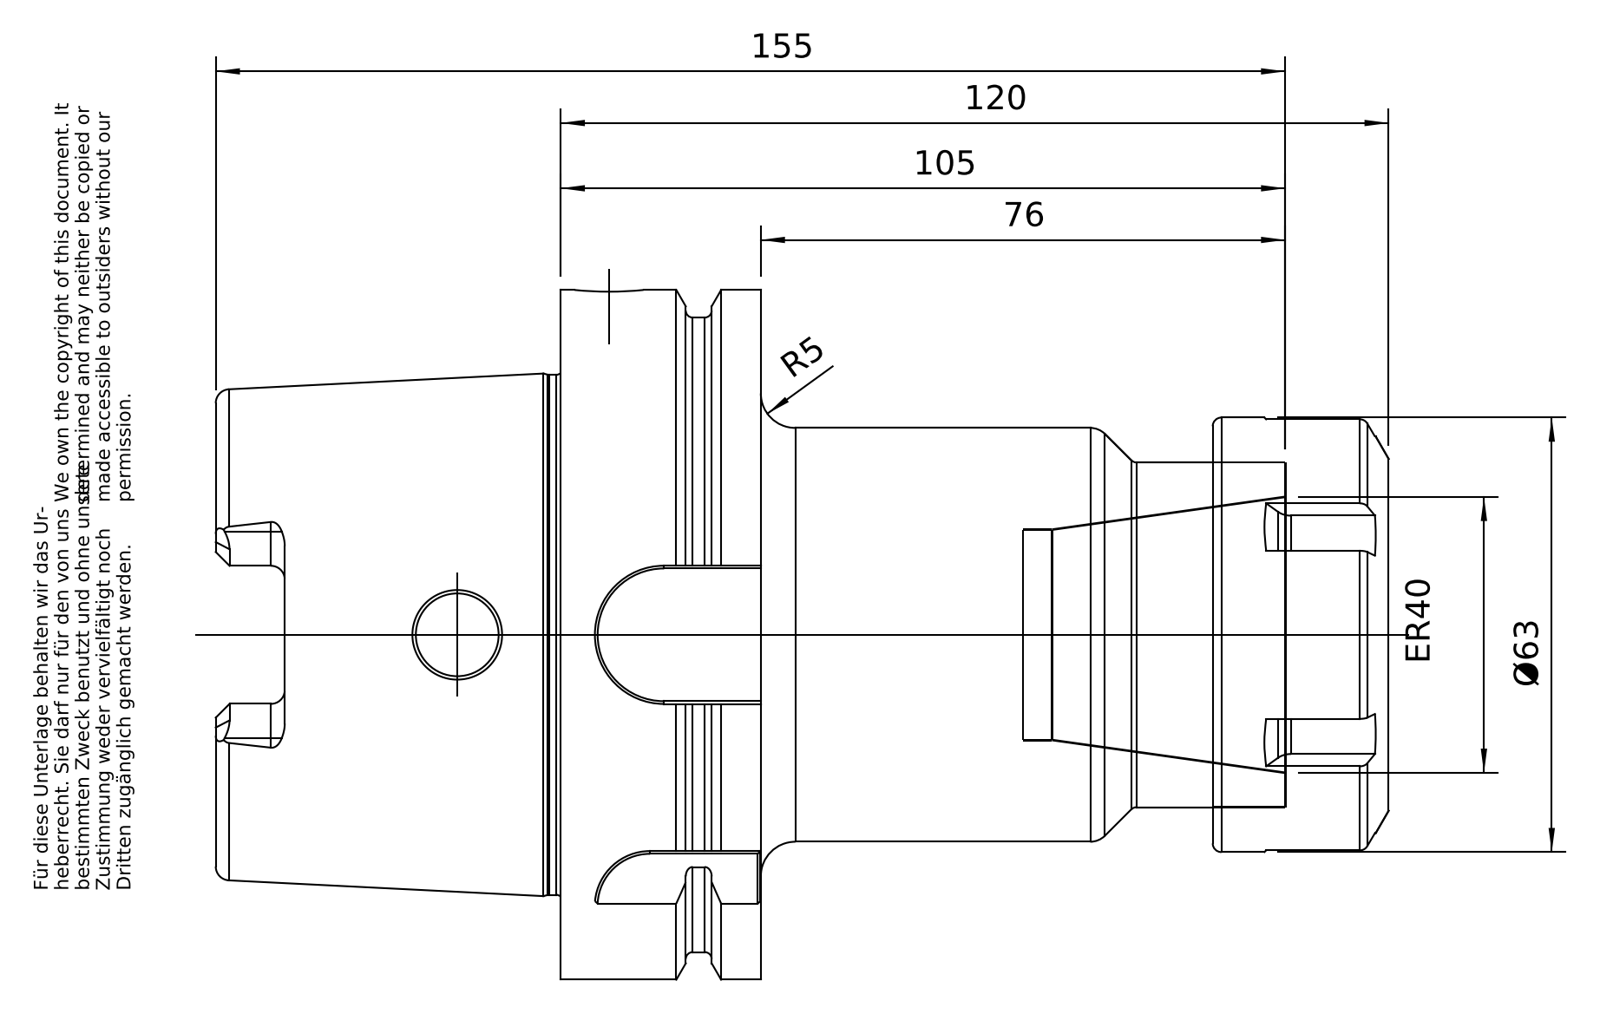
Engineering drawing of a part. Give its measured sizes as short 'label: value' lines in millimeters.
name: A100-020-40; 83-912-40; A100-020-40_ASM
written by: PRO/ENGINEER BY PARAMETRIC TECHNOLOGY CORPORATION, 2010430 (CONFIG_CONTROL_DESIGN)
unit: mm
bodies: 2 solids, 227 faces (80 planar, 60 cylindrical, 87 other)
size: 170 × 100 × 100
volume: 488 326 mm³; area: 77 515 mm²
holes: 1× ⌀10, 1× ⌀12, 1× ⌀22.5, 1× ⌀24, 1× ⌀24.32, 1× ⌀24.5, 1× ⌀30.5, 1× ⌀53, 1× ⌀63
bosses: 1× ⌀100, 1× ⌀92, 1× ⌀75.36, 1× ⌀60, 1× ⌀50
rounds: 6× R2, 6× R2.7, 4× R5, 1× R8, 1× R10.02, 1× R11.02
face distances: 29, 94.5, 65.5, 120, 91, 25.5, 12.5, 16.5, 82, 107.5
